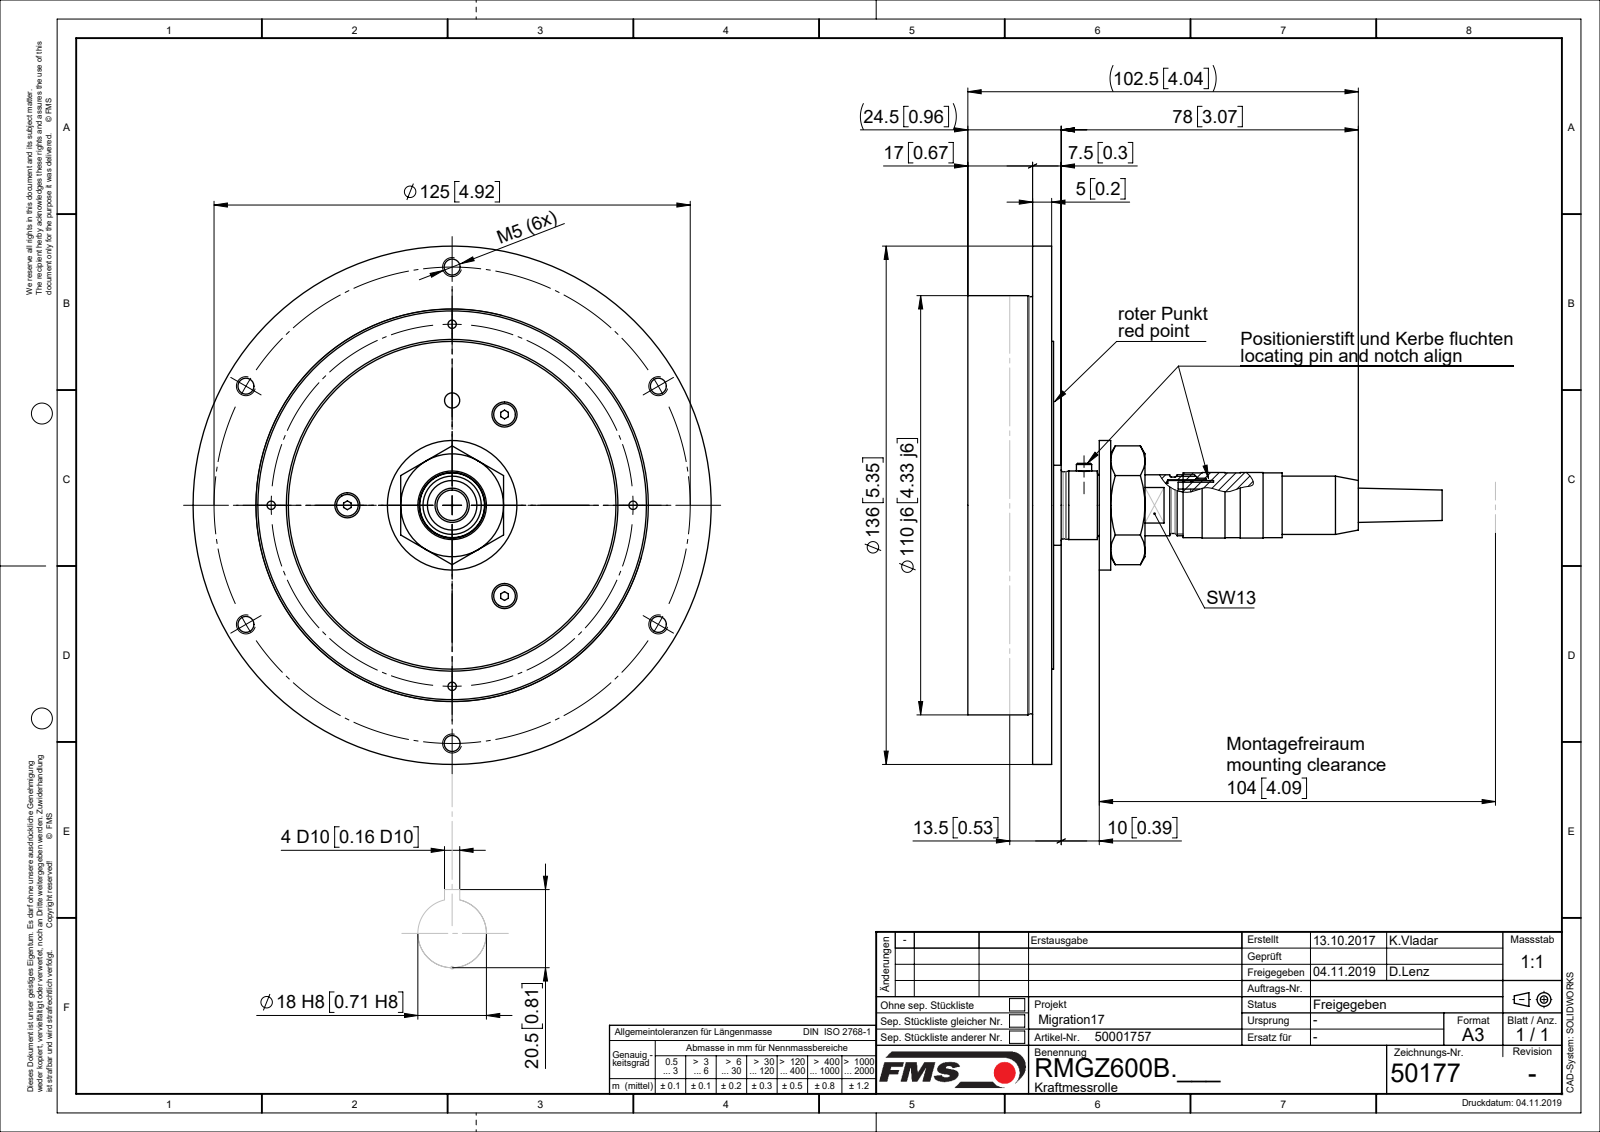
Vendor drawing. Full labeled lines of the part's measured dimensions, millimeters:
Part name (STEP PRODUCT): R50177; R4984204; R47423; TEIL1 (+8 more)
STEP written by: Mechanical Desktop 2007 (CONFIG_CONTROL_DESIGN)
Units: millimetres
Bodies: 12 solids, 303 faces (85 planar, 136 cylindrical, 82 other)
Overall size (bounding box): 136 × 136 × 124.5
Volume: 236 943 mm³ · Surface area: 106 049 mm²
Round holes (diameter × count): ⌀4.33 ×6, ⌀2.2 ×4, ⌀2.6 ×3, ⌀3.4 ×3, ⌀3 ×1, ⌀4 ×1, ⌀10 ×1, ⌀11.5 ×1, ⌀13.3 ×1, ⌀16.68 ×1, ⌀19 ×1, ⌀23 ×1
Round bosses / shafts (diameter × count): ⌀6 ×3, ⌀3 ×3, ⌀136 ×1, ⌀110 ×1, ⌀86 ×1, ⌀80 ×1, ⌀73 ×1, ⌀69 ×1
Main face-to-face distances: 5.5, 16.5, 17, 0.5, 2, 22, 18.5, 2.5, 3.5, 5
Hole centre spacings: 62.5, 108.25, 27.5, 41.05, 47.5, 54.89, 67.18, 68.28
